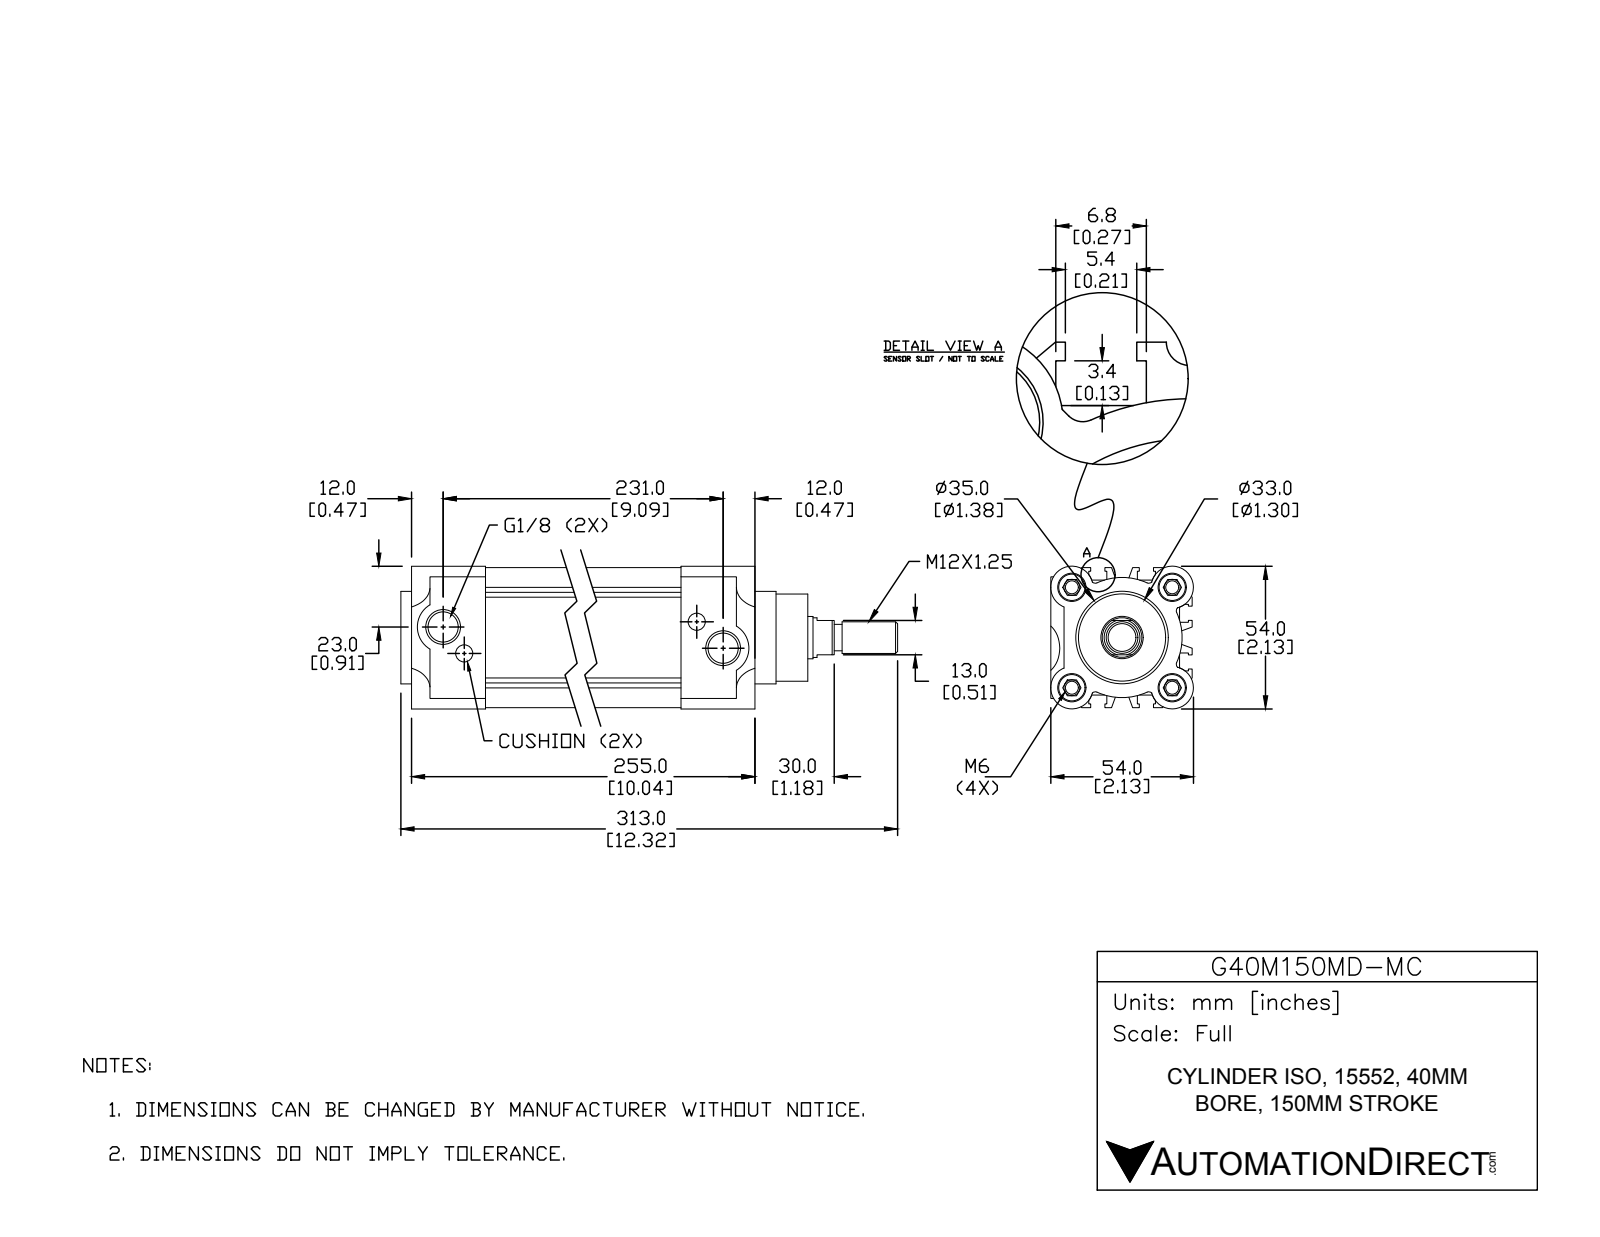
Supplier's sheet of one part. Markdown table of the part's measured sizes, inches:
| quantity | value |
| --- | --- |
| part name | 40121150-R; G40M150MD-MC; 40121-HR; 40-HL (+1 more) |
| STEP written by | SolidWorks 2015 (CONFIG_CONTROL_DESIGN) |
| units | inches |
| bodies | 4 solids, 418 faces (236 planar, 138 cylindrical, 44 other) |
| overall size | 12.323 × 2.126 × 2.126 |
| volume | 29.81 in³ |
| surface area | 229.9 in² |
| round holes (diameter × count) | 0.194 × 4, 0.421 × 4, 0.256 × 2, 0.451 × 2, 0.63 × 1 |
| round bosses / shafts (diameter × count) | 0.394 × 5, 1.575 × 1, 1.378 × 1, 1.299 × 1, 0.591 × 1, 0.472 × 1 |
| partial cylindrical surfaces (radius × count) | 0.059 × 12, 0.004 × 6, 0.295 × 4, 0.315 × 4, 0.384 × 2, 0.886 × 1, 0.896 × 1 |
| main face-to-face distances | 1.9, 0.187, 2.087, 0.724, 0.954, 1.372, 0.547, 1.539, 0.815, 1.272 |
| hole center spacings | 1.058, 1.496, 2.116, 0.504, 0.557, 8.399, 8.701, 8.78 |
